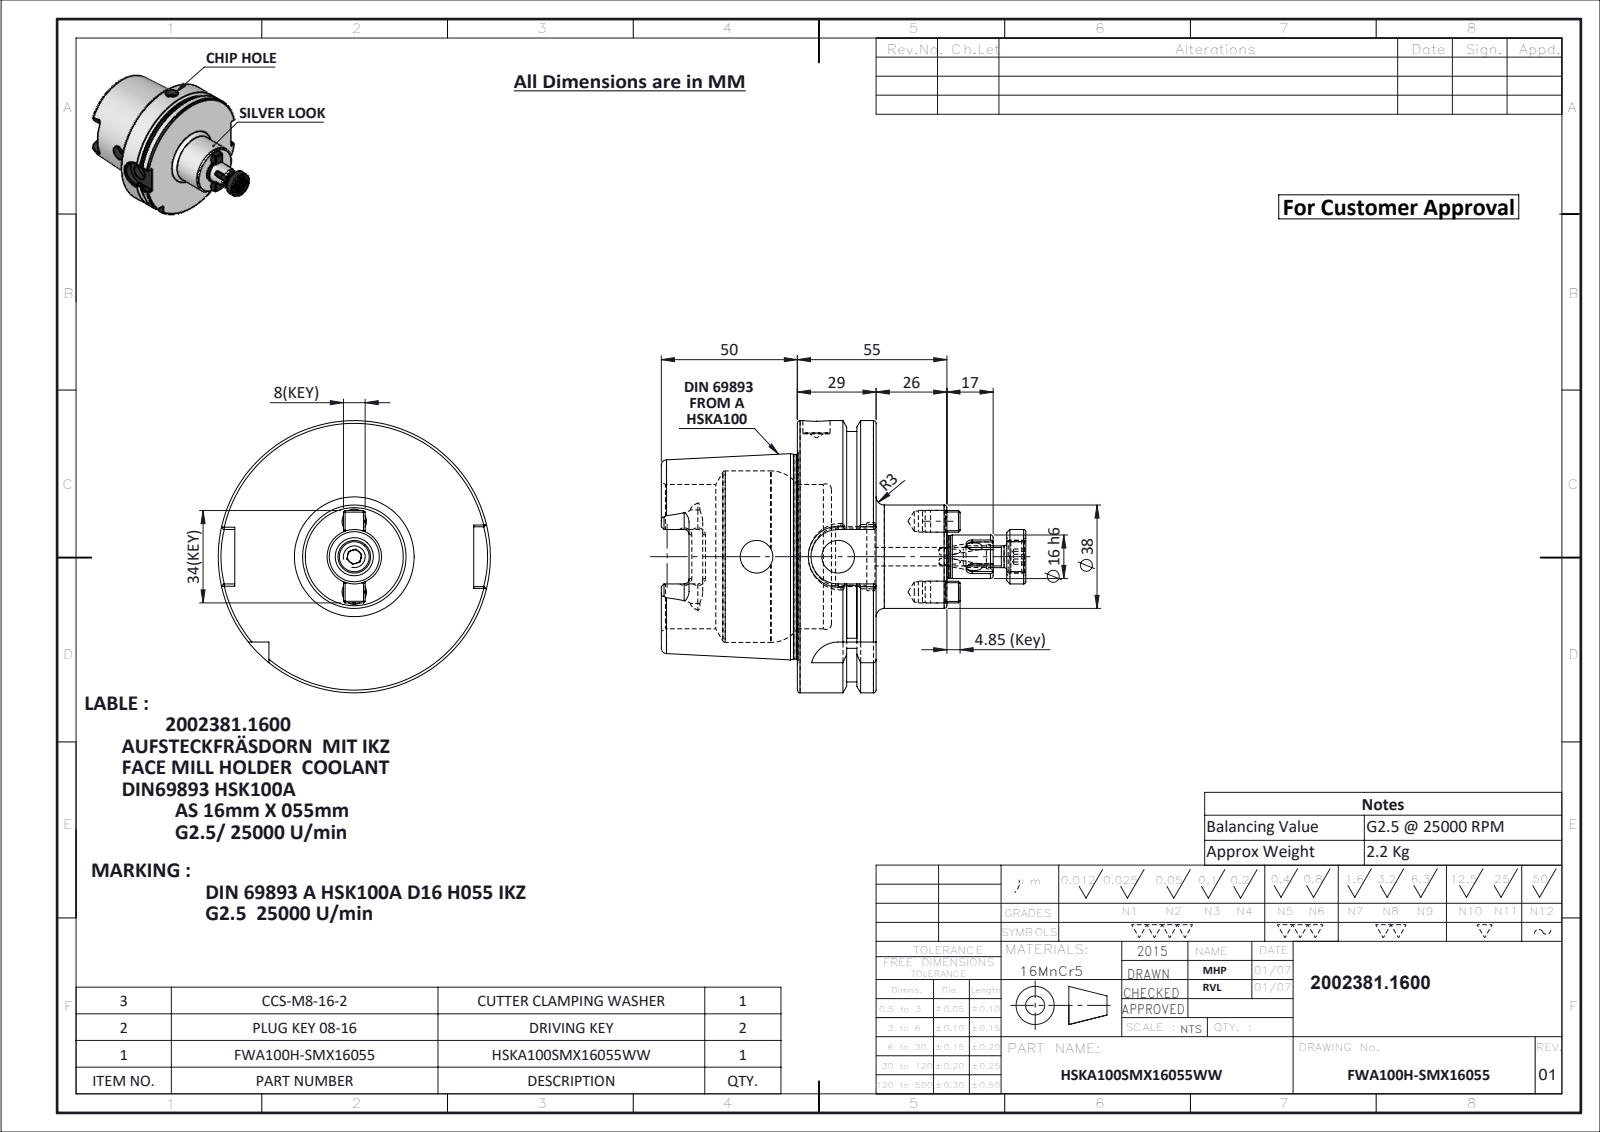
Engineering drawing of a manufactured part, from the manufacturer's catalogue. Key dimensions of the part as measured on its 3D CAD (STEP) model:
Part name (STEP PRODUCT): CCS-M8-16-1; PLUG KEY 08-16; CCS-M8-16-2; HSKA100SMX16055WW (+2 more)
STEP written by: SolidWorks 2024 (CONFIG_CONTROL_DESIGN)
Units: millimetres
Bodies: 5 solids, 361 faces (118 planar, 100 cylindrical, 143 other)
Overall size (bounding box): 133.95 × 100 × 100
Volume: 287 707 mm³ · Surface area: 58 278 mm²
Round holes (diameter × count): ⌀3 ×4, ⌀7.5 ×2, ⌀8 ×2, ⌀12 ×2, ⌀6.8 ×1, ⌀9 ×1, ⌀10 ×1, ⌀11 ×1, ⌀21 ×1, ⌀25 ×1, ⌀53 ×1, ⌀63 ×1
Round bosses / shafts (diameter × count): ⌀8.02 ×2, ⌀7.98 ×2, ⌀100 ×1, ⌀92 ×1, ⌀75.16 ×1, ⌀38 ×1, ⌀20 ×1, ⌀16 ×1
Partial cylindrical surfaces — rounded edges, fillets, slot ends (radius × count): R1.8 ×6, R2 ×4, R4.88 ×4, R5.25 ×2, R10 ×2, R11 ×1
Main face-to-face distances: 28.95, 12.5, 16.45, 50, 62.5, 78.95, 26, 104.95, 54.95, 42.45
Hole centre spacings: 13, 26, 30
